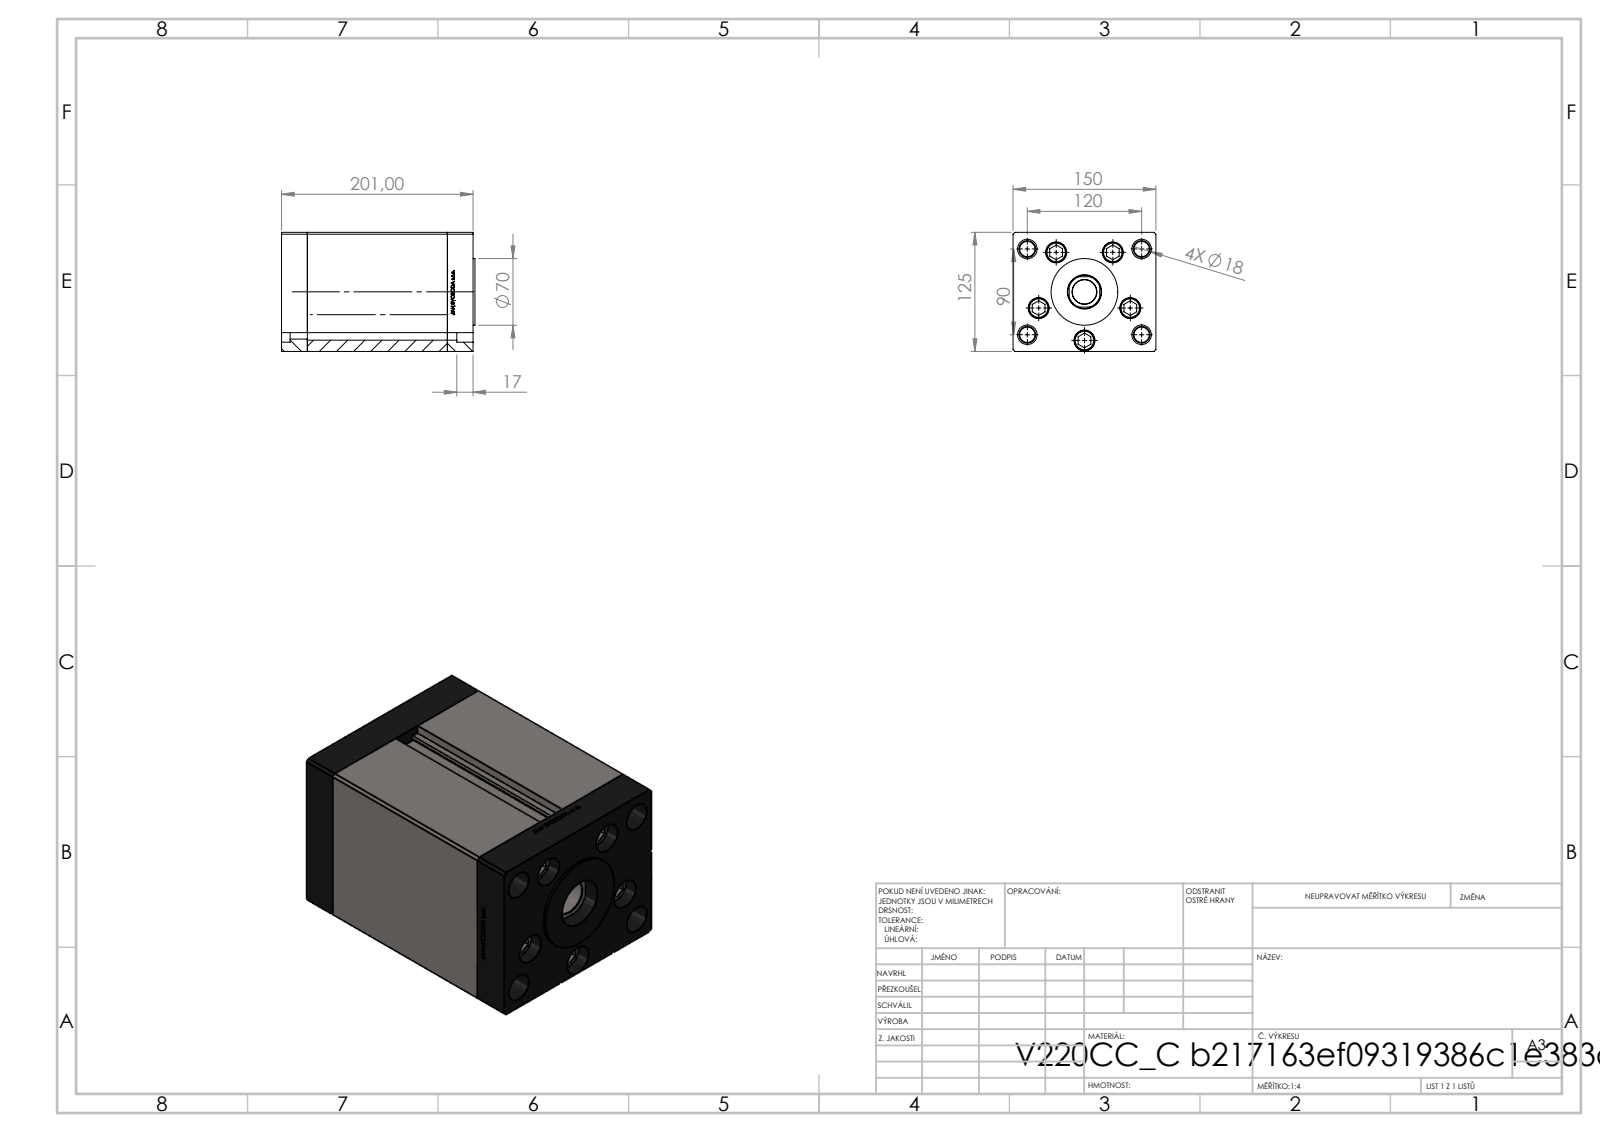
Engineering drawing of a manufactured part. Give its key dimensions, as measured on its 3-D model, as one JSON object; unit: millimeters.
{"part_name": "V220C FRONT; ALLEN BOLT; V220C_C MIDDLE; V220C_VC_C (+1 more)", "step_written_by": "SolidWorks 2019 (CONFIG_CONTROL_DESIGN)", "units": "millimeters", "bodies": {"solids": 13, "faces": 1159, "planar": 538, "cylindrical": 159, "other": 462}, "overall_size": [203, 150, 125], "volume_mm3": 3058000, "surface_area_mm2": 372685, "round_holes": [[17.5, 9], [22, 5], [16, 4], [20.5, 4], [21, 1], [25.5, 1], [36, 1]], "round_bosses_or_shafts": [[8, 5], [21, 4], [80, 1], [70, 1]], "partial_cylinders_radius": [[0.93, 2], [17.5, 1]], "face_to_face_distances": [27, 174, 125, 150, 147, 201, 7.8, 166.2, 139.2, 34.8], "hole_center_spacings": [51, 75, 30.43, 30.48, 58.89, 60.3, 61.25, 63.14]}
